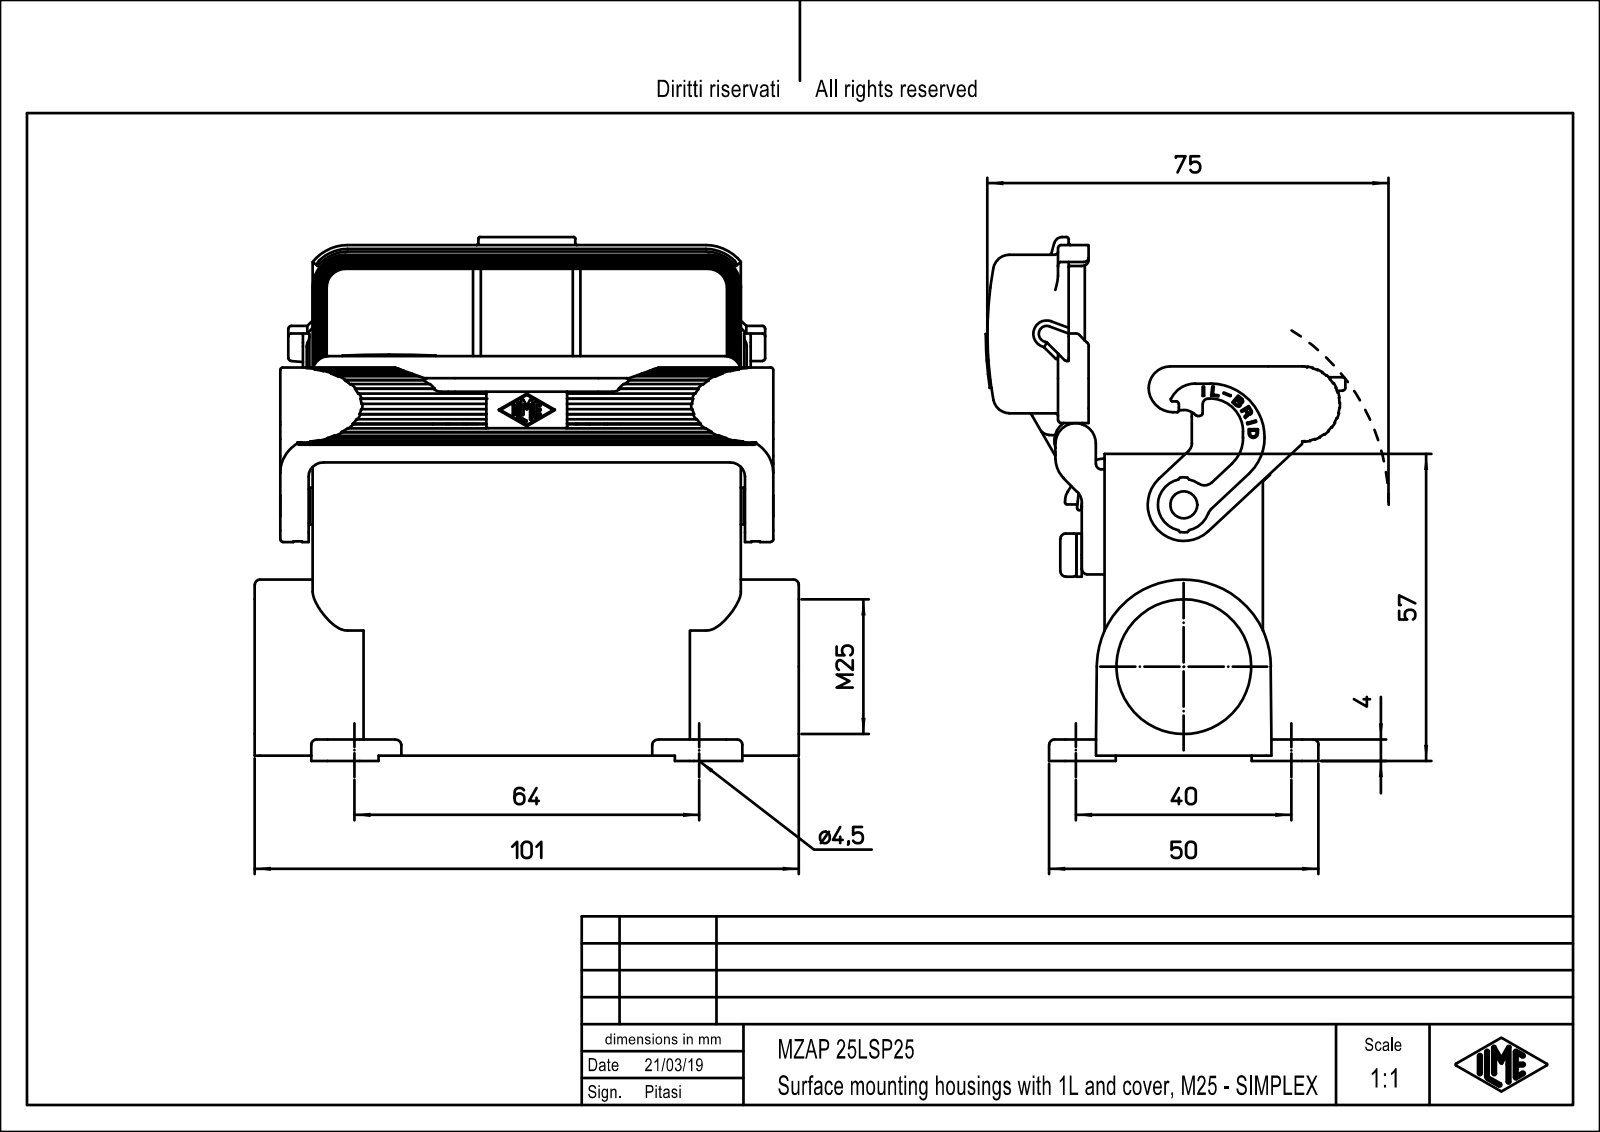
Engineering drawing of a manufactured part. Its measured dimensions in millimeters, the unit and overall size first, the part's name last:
Units: millimetres
Overall size (bounding box): 101 × 97.03 × 66.47
Round holes (diameter × count): ⌀3 ×4, ⌀4.5 ×4, ⌀20 ×1, ⌀25 ×1
Round bosses / shafts (diameter × count): ⌀0.8 ×3, ⌀8.4 ×1, ⌀8 ×1, ⌀6.8 ×1, ⌀4.8 ×1, ⌀2.4 ×1
Partial cylindrical surfaces — rounded edges, fillets, slot ends (radius × count): R3 ×13, R3.5 ×12, R0.5 ×7, R6.5 ×7, R1.5 ×4, R2 ×4, R3.2 ×4, R3.4 ×4
Main face-to-face distances: 2.76, 29.4, 26.65, 23.89, 2.75, 3, 26.64, 2.6, 26.8, 3.8
Hole centre spacings: 12.04, 28.02, 66.1, 70.77, 16, 40, 64, 66
Volume: 90 781 mm³ · Surface area: 55 796 mm²
Bodies: 1 solid, 537 faces (293 planar, 214 cylindrical, 30 other)
Part name (STEP PRODUCT): MZAP_25_LSP25
STEP written by: PTC Creo Elements/Direct Modeling 19.0E 27-Jun-2016 (C) Parametric Technology GmbH (AUTOMOTIVE_DESIGN)
